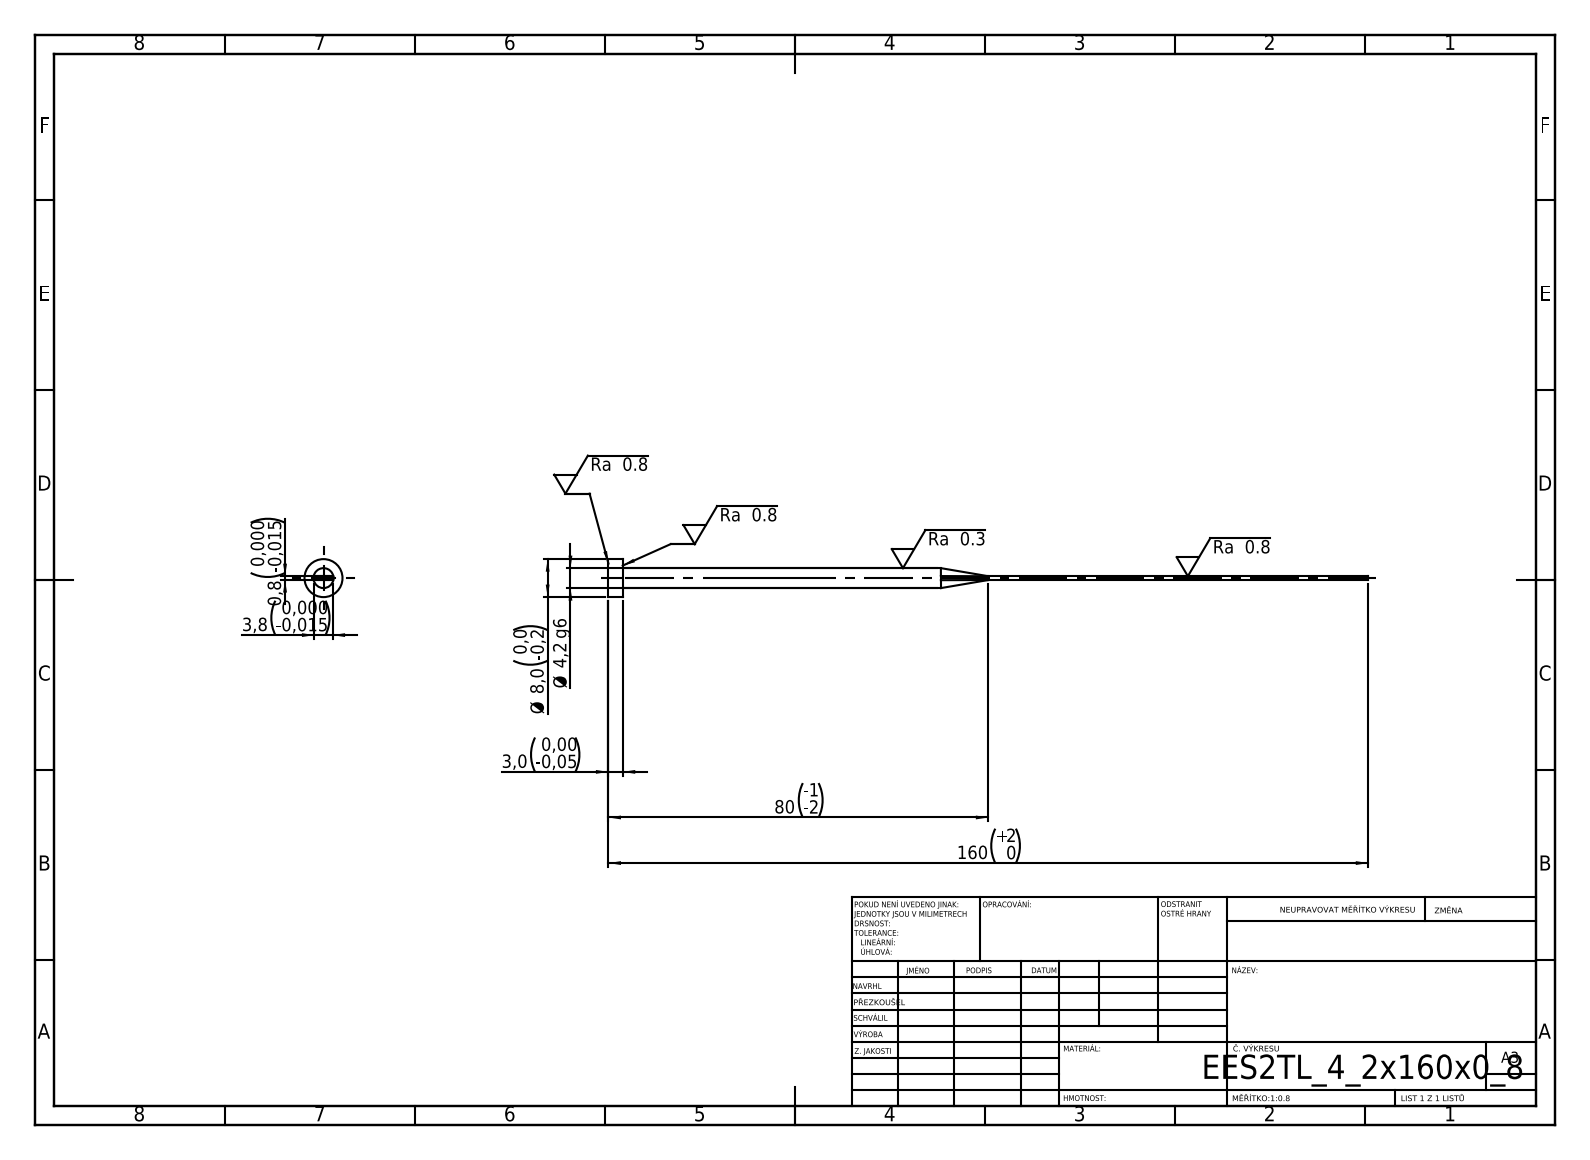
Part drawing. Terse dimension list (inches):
written by: SolidWorks 2019 (CONFIG_CONTROL_DESIGN)
unit: in
bodies: 1 solid, 15 faces (7 planar, 4 cylindrical, 4 other)
size: 6.299 × 0.315 × 0.315
volume: 0.086 in³; area: 2.934 in²
bosses: 1× ⌀0.315, 1× ⌀0.165
face distances: 0.031, 0.15, 0.118, 6.299, 6.181
